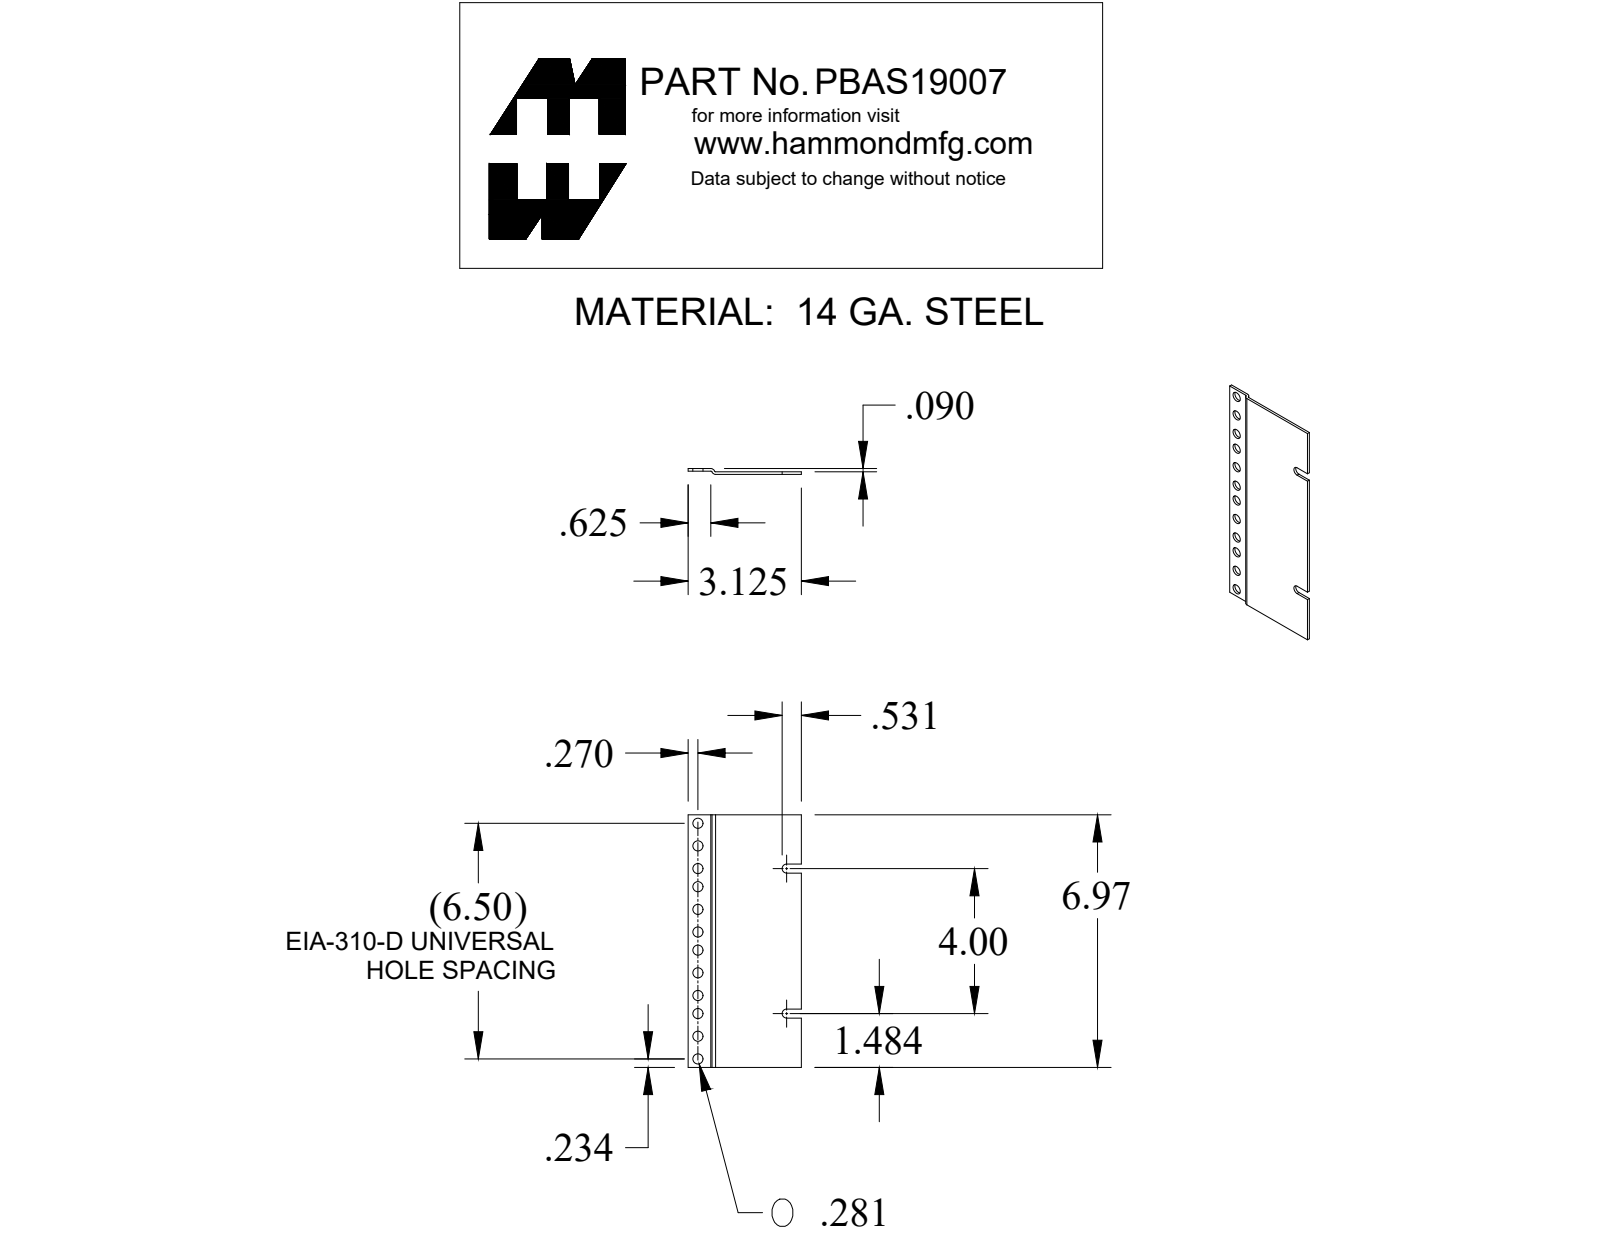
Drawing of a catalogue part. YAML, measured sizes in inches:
part_name: "PBAS19007BK2"
step_written_by: "SolidWorks 2019 (CONFIG_CONTROL_DESIGN)"
units: inches
bodies: {solids: 1, faces: 32, planar: 14, cylindrical: 18, other: 0}
overall_size: [6.968, 3.125, 0.162]
volume: 1.515
surface_area: 44.44
round_holes:
  - {diameter: 0.281, count: 12}
partial_cylinders:
  - {radius: 0.036, count: 2}
  - {radius: 0.108, count: 2}
  - {radius: 0.125, count: 2}
face_to_face_distances: [0.072, 0.09, 0.162, 0.018, 0.09, 0.072, 3.125, 6.968, 1.359, 5.609]
hole_center_spacings: [1.75, 0.625, 0.625, 1.125, 1.25, 2.375, 2.875, 3.5]
